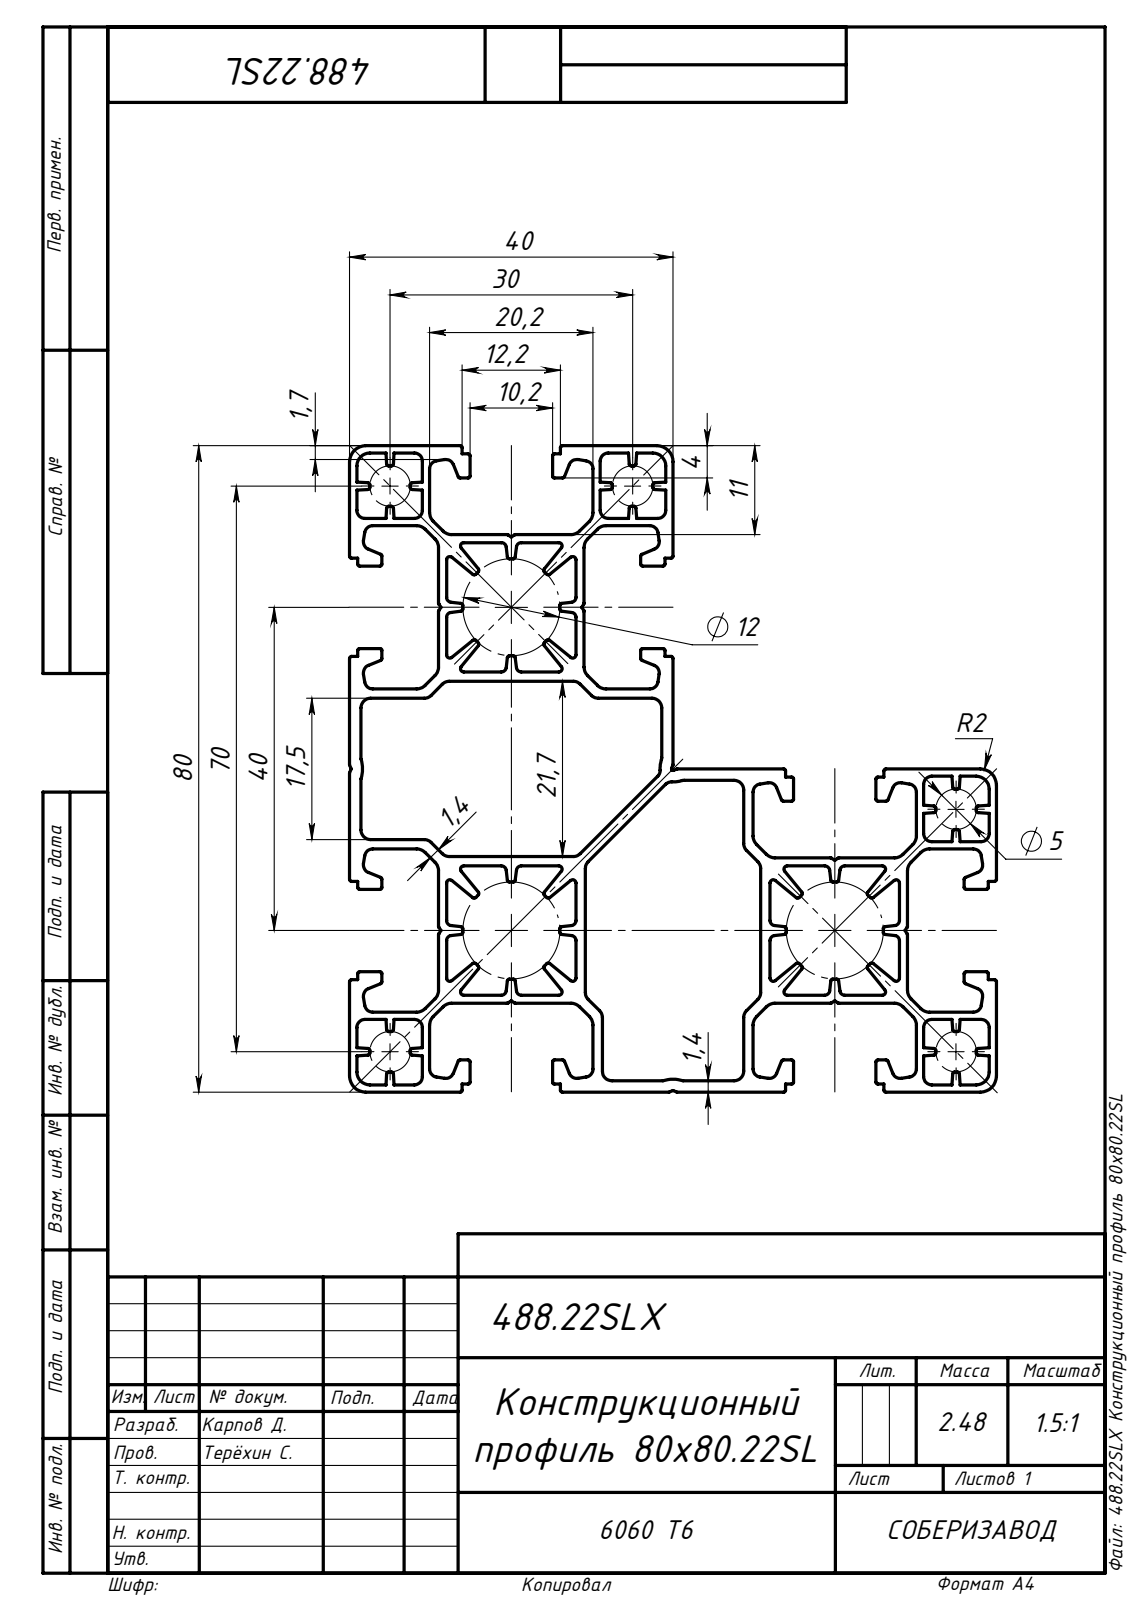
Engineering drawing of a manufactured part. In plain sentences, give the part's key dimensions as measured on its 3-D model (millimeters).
Its 3-D file was written by "SolidWorks 2019 (AUTOMOTIVE_DESIGN)". It is 1 solid with 790 faces: 404 planar, 386 cylindrical and 0 other. Overall it measures 1000 by 80 by 80 millimeters. Its volume is 918 031 cubic millimeters and its surface area 1 390 000 square millimeters. Partial cylindrical surfaces (rounded edges, fillets, slot ends): 173 of radius 0.25, 51 of radius 1, 32 of radius 1.5, 24 of radius 0.4, 24 of radius 0.6, 20 of radius 1.2, 5 of radius 1.6, 5 of radius 2. The main face-to-face distances are 40, 12, 28, 11, 2.1, 29, 9.9, 30.1, 17, 1.
